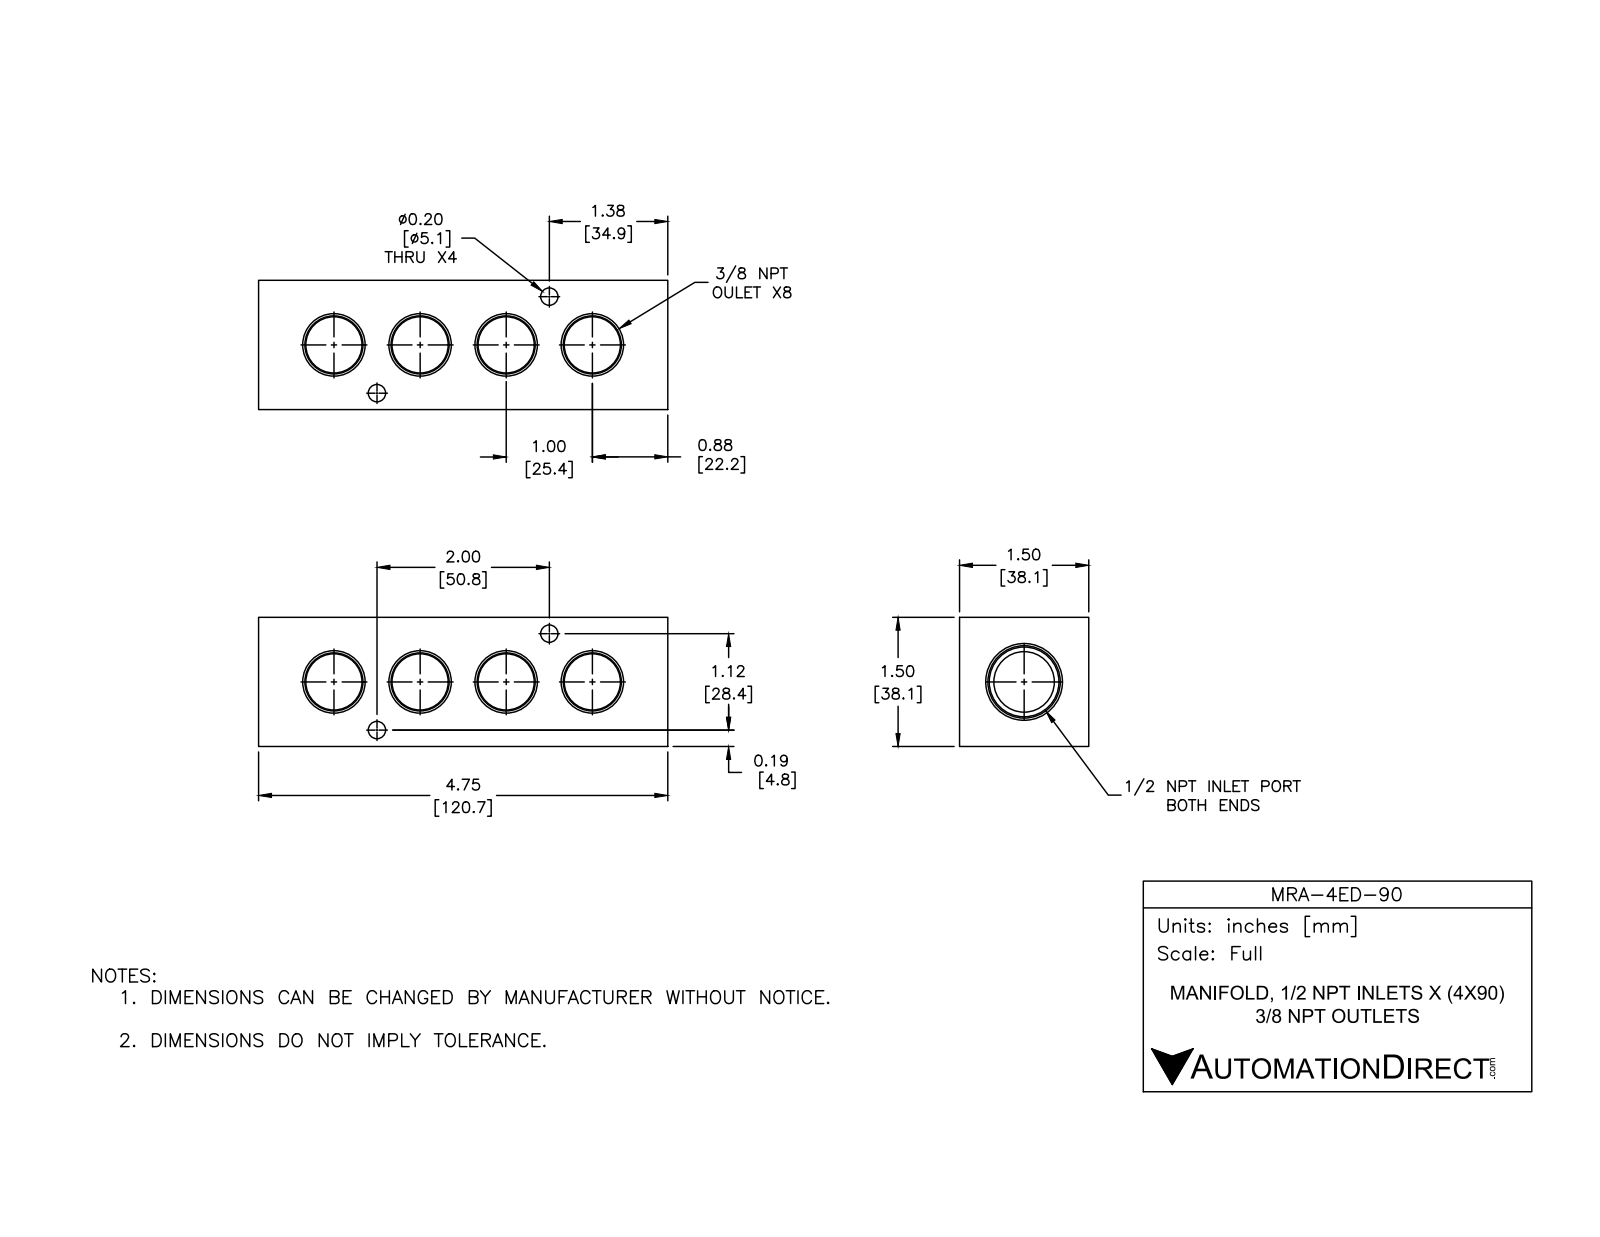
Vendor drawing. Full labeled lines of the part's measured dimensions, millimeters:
Part name (STEP PRODUCT): MRA-4ED-90
STEP written by: SolidWorks 2015 (CONFIG_CONTROL_DESIGN)
Units: millimetres
Bodies: 1 solid, 98 faces (24 planar, 34 cylindrical, 40 other)
Overall size (bounding box): 120.7 × 38.1 × 38.1
Volume: 120 100 mm³ · Surface area: 31 530 mm²
Round holes (diameter × count): ⌀14.3 ×8, ⌀5.1 ×4, ⌀17.9 ×1
Main face-to-face distances: 38.1, 120.7, 27.7, 10.4, 13.5, 107.2, 93.7
Hole centre spacings: 19.1, 25.4, 40.7, 50.8, 65.1, 58.2, 76.2
